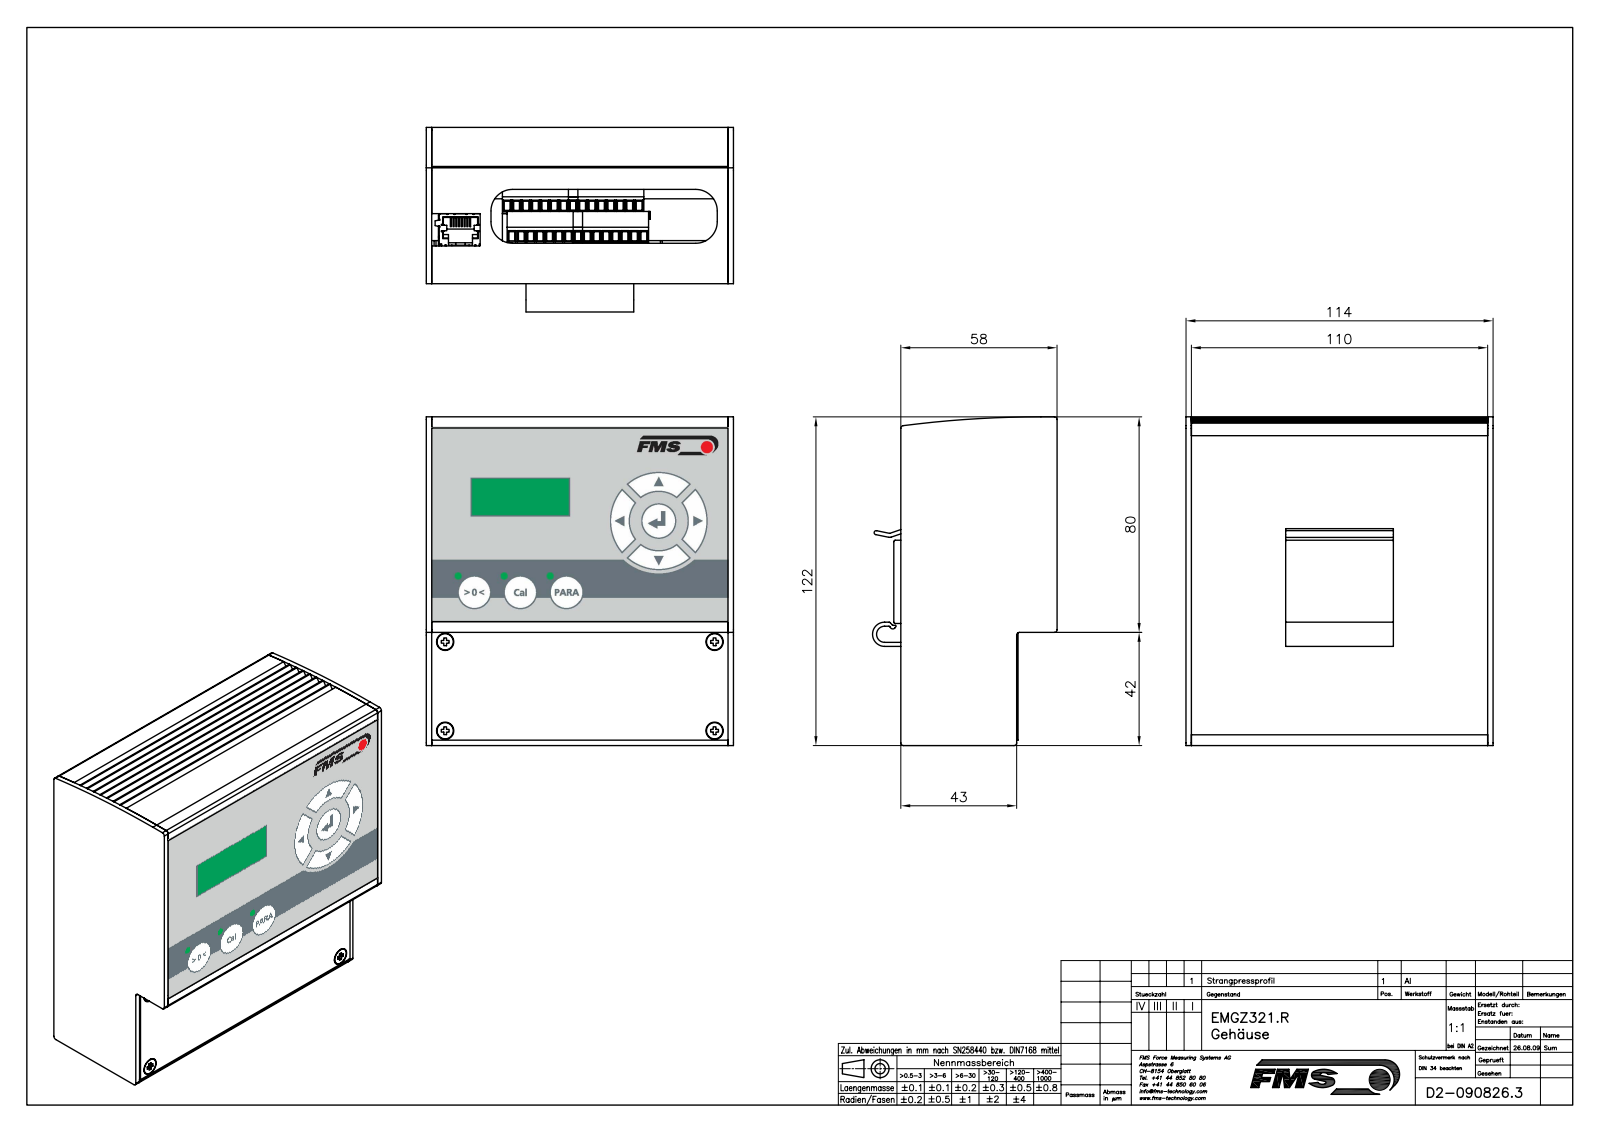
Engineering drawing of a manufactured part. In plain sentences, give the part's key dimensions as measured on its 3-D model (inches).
The part is named "E0908263; E0801092; E0708103; E0708203 (+7 more)". Its 3-D file was written by "Mechanical Desktop 2009 (CONFIG_CONTROL_DESIGN)". It is 19 solids with 1780 faces: 1420 planar, 279 cylindrical and 81 other. Overall it measures 4.803 by 4.488 by 2.697 inches. Its volume is 12.54 cubic inches and its surface area 241.4 square inches. Round holes: 30 of diameter 0.118, 6 of diameter 0.126, 5 of diameter 0.102, 4 of diameter 0.039, 4 of diameter 0.094, 3 of diameter 0.138, 2 of diameter 0.079, 2 of diameter 0.217. Round bosses or shafts: 5 of diameter 0.118, 4 of diameter 0.236, 2 of diameter 0.22, 2 of diameter 0.114, 2 of diameter 0.105. Partial cylindrical surfaces (rounded edges, fillets, slot ends): 19 of radius 0.01, 15 of radius 0.039, 8 of radius 0.157, 6 of radius 0.059, 5 of radius 0.02, 4 of radius 0.004, 4 of radius 0.014, 4 of radius 0.315. The main face-to-face distances are 0.079, 4.409, 0.118, 0.315, 0.433, 0.063, 0.252, 0.37, 0.591, 0.098. The hole center spacings are 0.34, 0.138, 0.392, 0.276, 0.479, 0.413, 0.586, 0.551.
